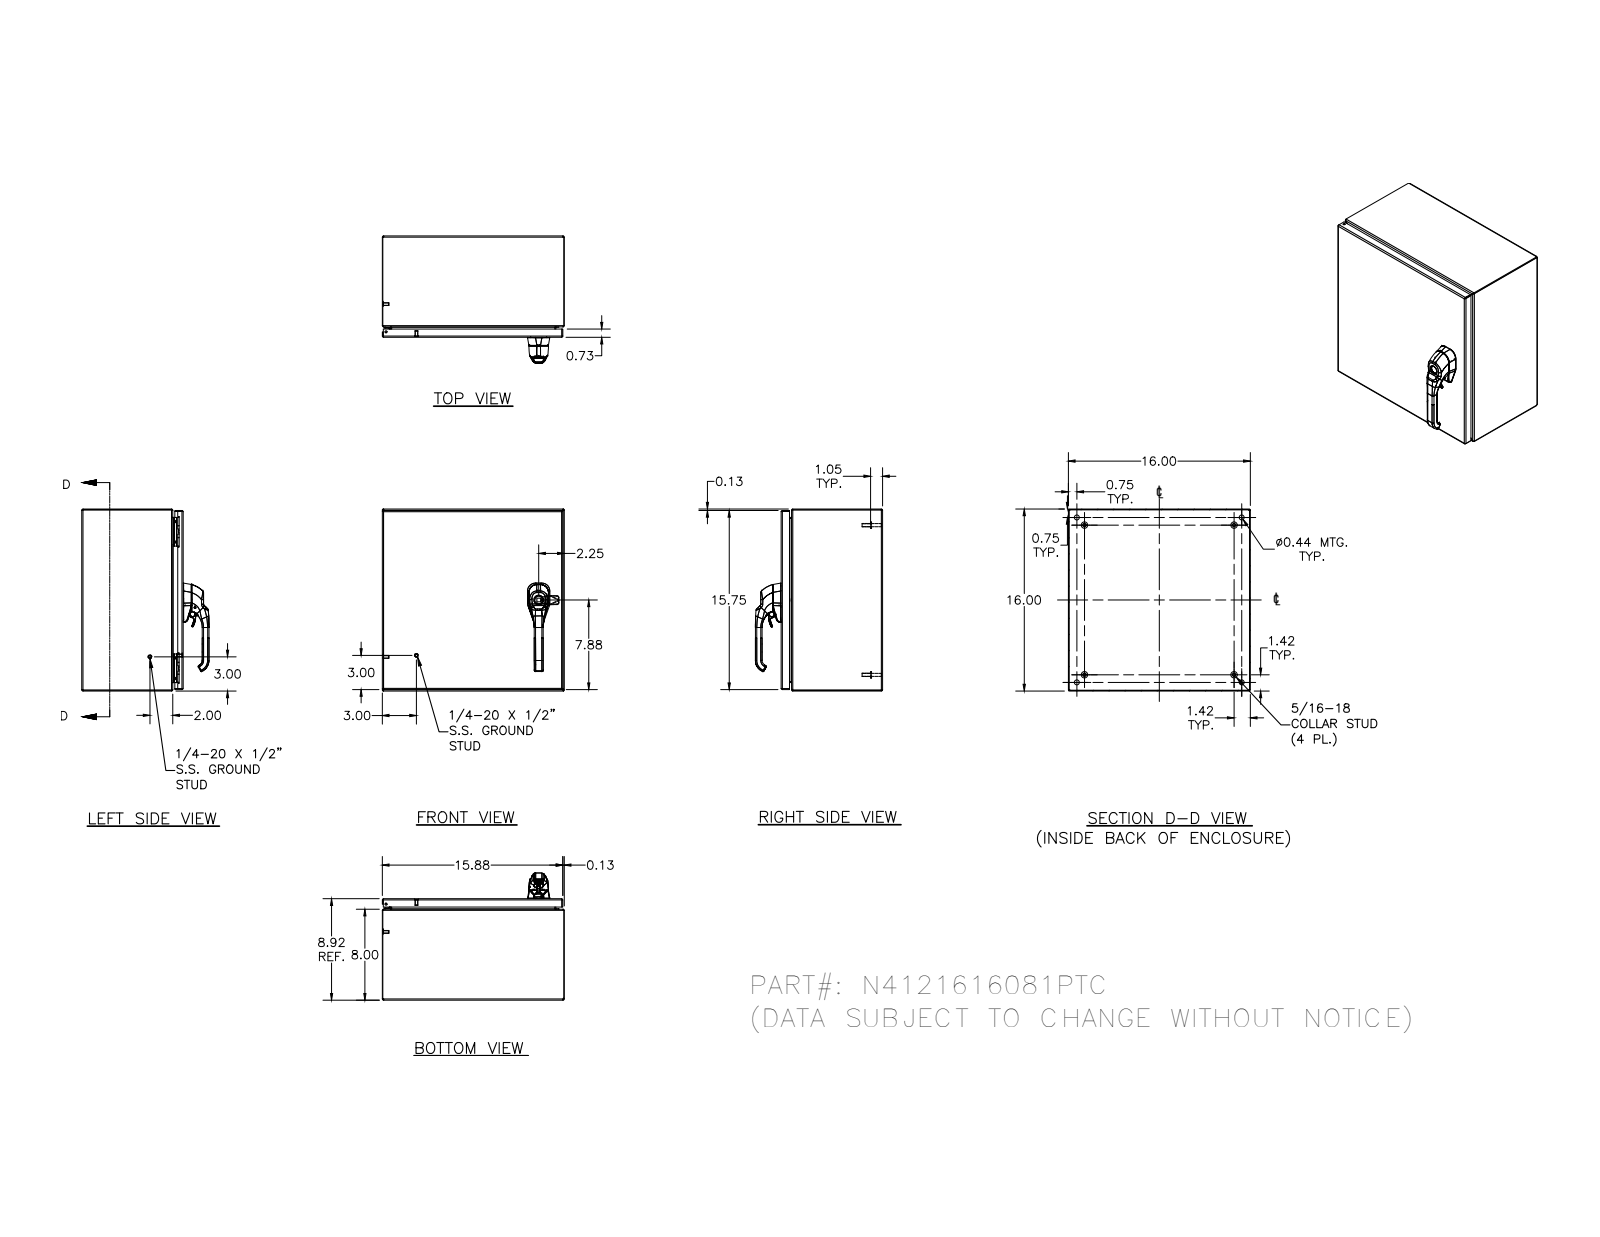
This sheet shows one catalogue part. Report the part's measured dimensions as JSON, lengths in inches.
{"part_name": "N4121616081PTC", "step_written_by": "SolidWorks 2018 (AUTOMOTIVE_DESIGN)", "units": "inches", "bodies": {"solids": 28, "faces": 1280, "planar": 417, "cylindrical": 474, "other": 389}, "overall_size": [16, 16, 11.095], "volume_in3": 95.13, "surface_area_in2": 2364, "round_holes": [[0.188, 5], [0.093, 4], [0.152, 4], [0.167, 4], [0.172, 4], [0.437, 4], [0.28, 3], [0.156, 2], [0.187, 1]], "round_bosses_or_shafts": [[0.25, 10], [0.563, 4], [0.36, 4], [0.32, 4], [0.3, 4], [0.275, 4], [0.256, 4], [0.164, 4]], "partial_cylinders_radius": [[0.031, 30], [0.05, 26], [0.105, 20], [0.016, 18], [0.125, 14], [0.032, 8], [0.067, 8], [0.068, 8]], "face_to_face_distances": [0.074, 15.926, 8.843, 8.917, 15.852, 16, 8.769, 7.926, 0.917, 0.739], "hole_center_spacings": [11.996, 14.5, 0.017, 0.66, 12.656, 0.019, 0.5, 0.648]}
